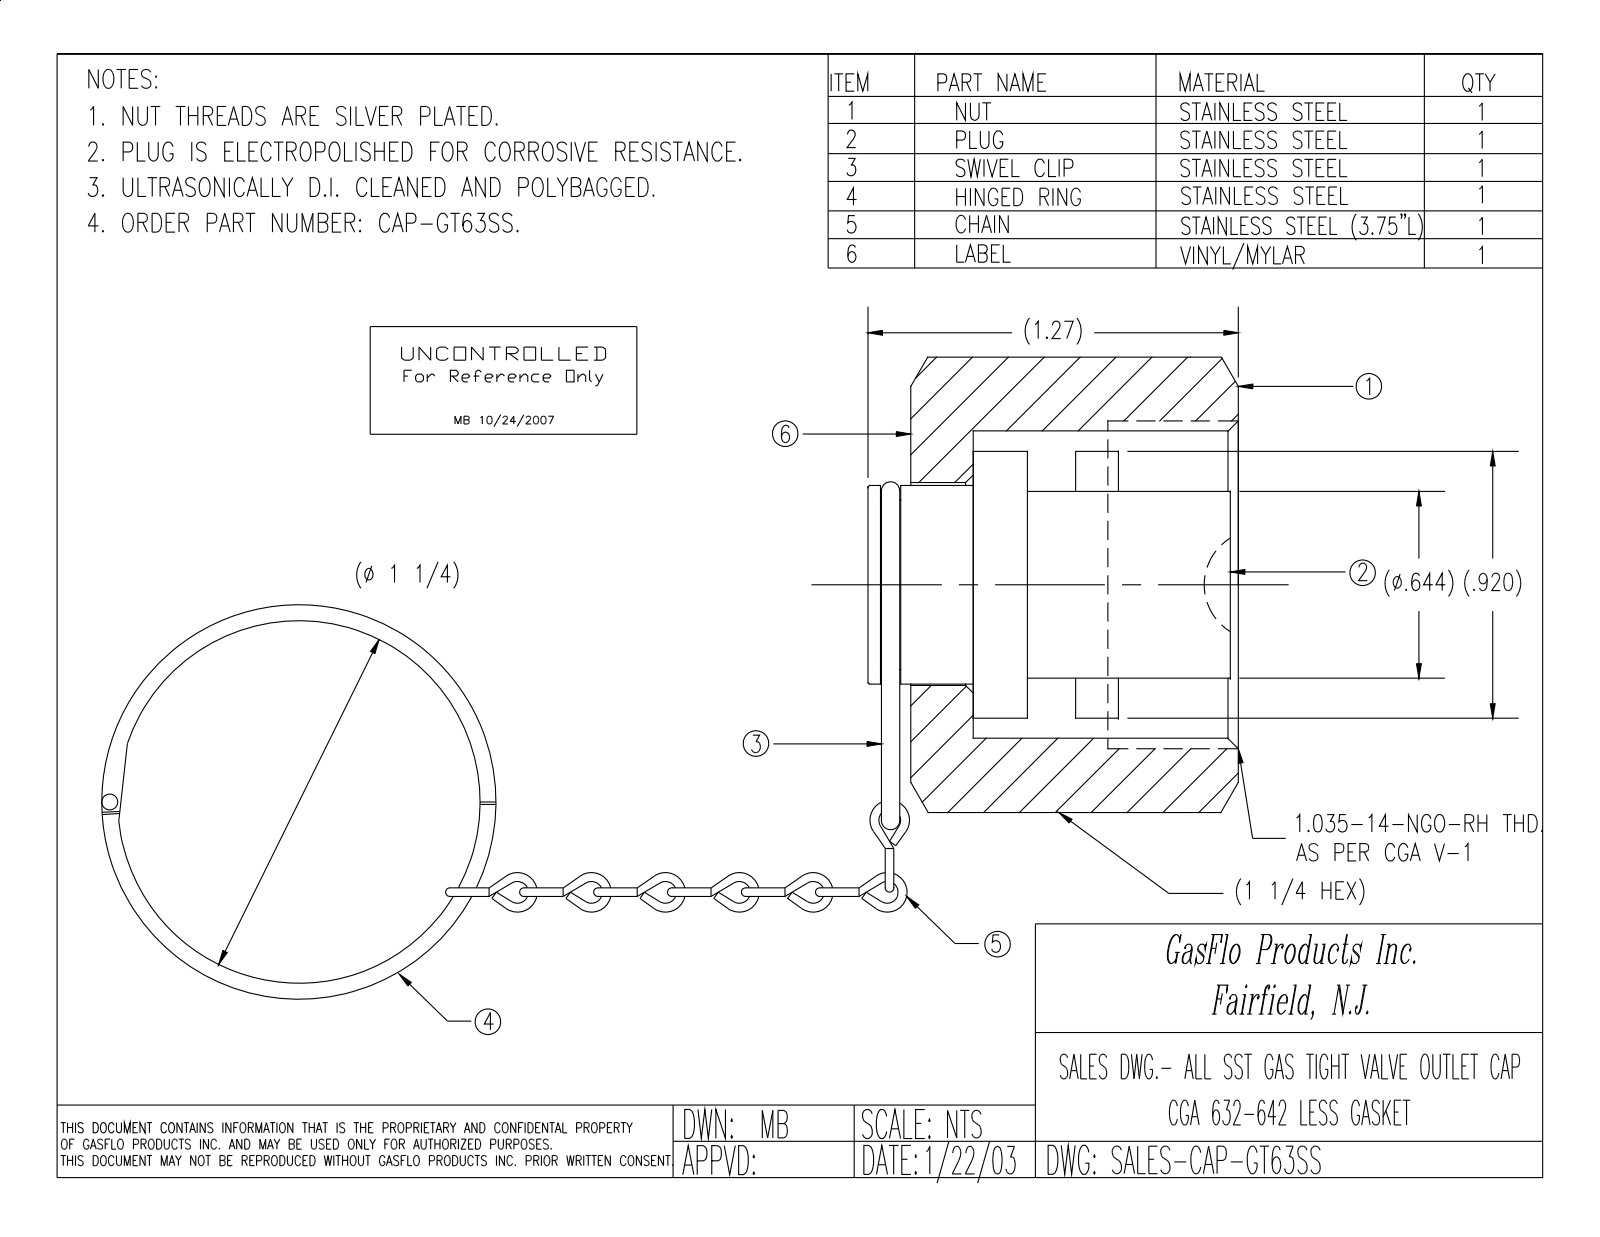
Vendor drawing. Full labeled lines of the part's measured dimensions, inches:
Part name (STEP PRODUCT): CAP-GT63SS; PRT-000403; PRT-000988; ASY-000709 (+7 more)
STEP written by: SolidWorks 2018 (CONFIG_CONTROL_DESIGN)
Units: inches
Bodies: 14 solids, 584 faces (211 planar, 164 cylindrical, 209 other)
Overall size (bounding box): 5.875 × 1.879 × 1.416
Volume: 1.287 in³ · Surface area: 20.56 in²
Round holes (diameter × count): ⌀0.063 ×1, ⌀0.078 ×1, ⌀0.149 ×1, ⌀0.333 ×1, ⌀0.577 ×1, ⌀0.697 ×1, ⌀0.962 ×1
Round bosses / shafts (diameter × count): ⌀0.063 ×32, ⌀0.92 ×1, ⌀0.685 ×1, ⌀0.644 ×1, ⌀0.585 ×1, ⌀0.501 ×1, ⌀0.15 ×1, ⌀0.145 ×1
Partial cylindrical surfaces — rounded edges, fillets, slot ends (radius × count): R0.005 ×24, R0.25 ×4, R0.01 ×2, R0.19 ×1
Main face-to-face distances: 1.25, 1.25, 0.222, 0.141, 0.363, 0.907, 1.13, 1.27, 0.55, 0.72
